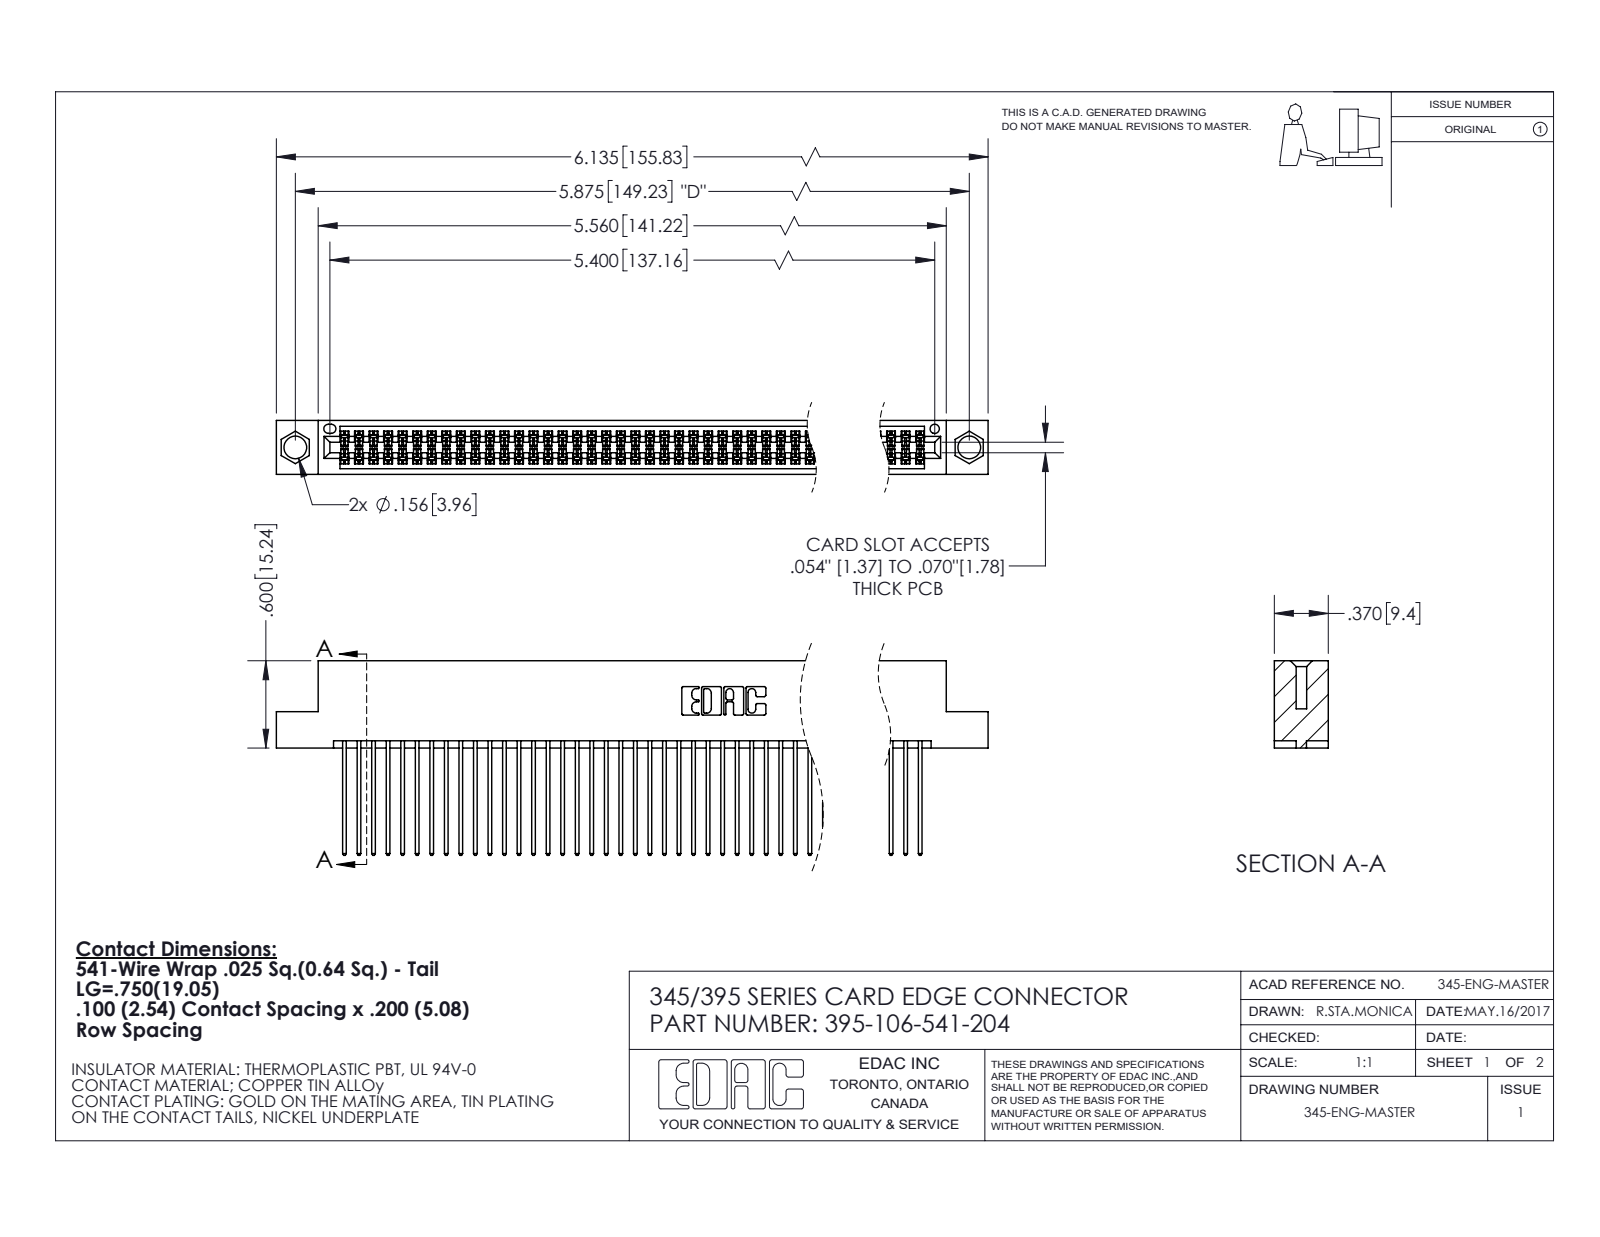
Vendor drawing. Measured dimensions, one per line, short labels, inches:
name: 345-292-001_345-293-141; 395-106-541-204; 345 Part_Flush Mounting Lugs - 0.156 Dia-TI
written by: SolidWorks 2020 (CONFIG_CONTROL_DESIGN)
unit: in
bodies: 107 solids, 5440 faces (3592 planar, 1848 cylindrical, 0 other)
size: 6.135 × 1.337 × 0.37
volume: 0.961 in³; area: 40.6 in²
holes: 2× ⌀0.156, 1× ⌀0.064
rounds: 159× R0.006, 106× R0.01, 22× R0.01, 6× R0.007, 6× R0.031, 3× R0.026, 2× R0.014, 2× R0.019
face distances: 0.298, 0.072, 0.2, 0.098, 0.272, 0.025, 0.225, 0.37, 0.175, 0.149
hole spacings: 0.27, 5.639, 5.875
